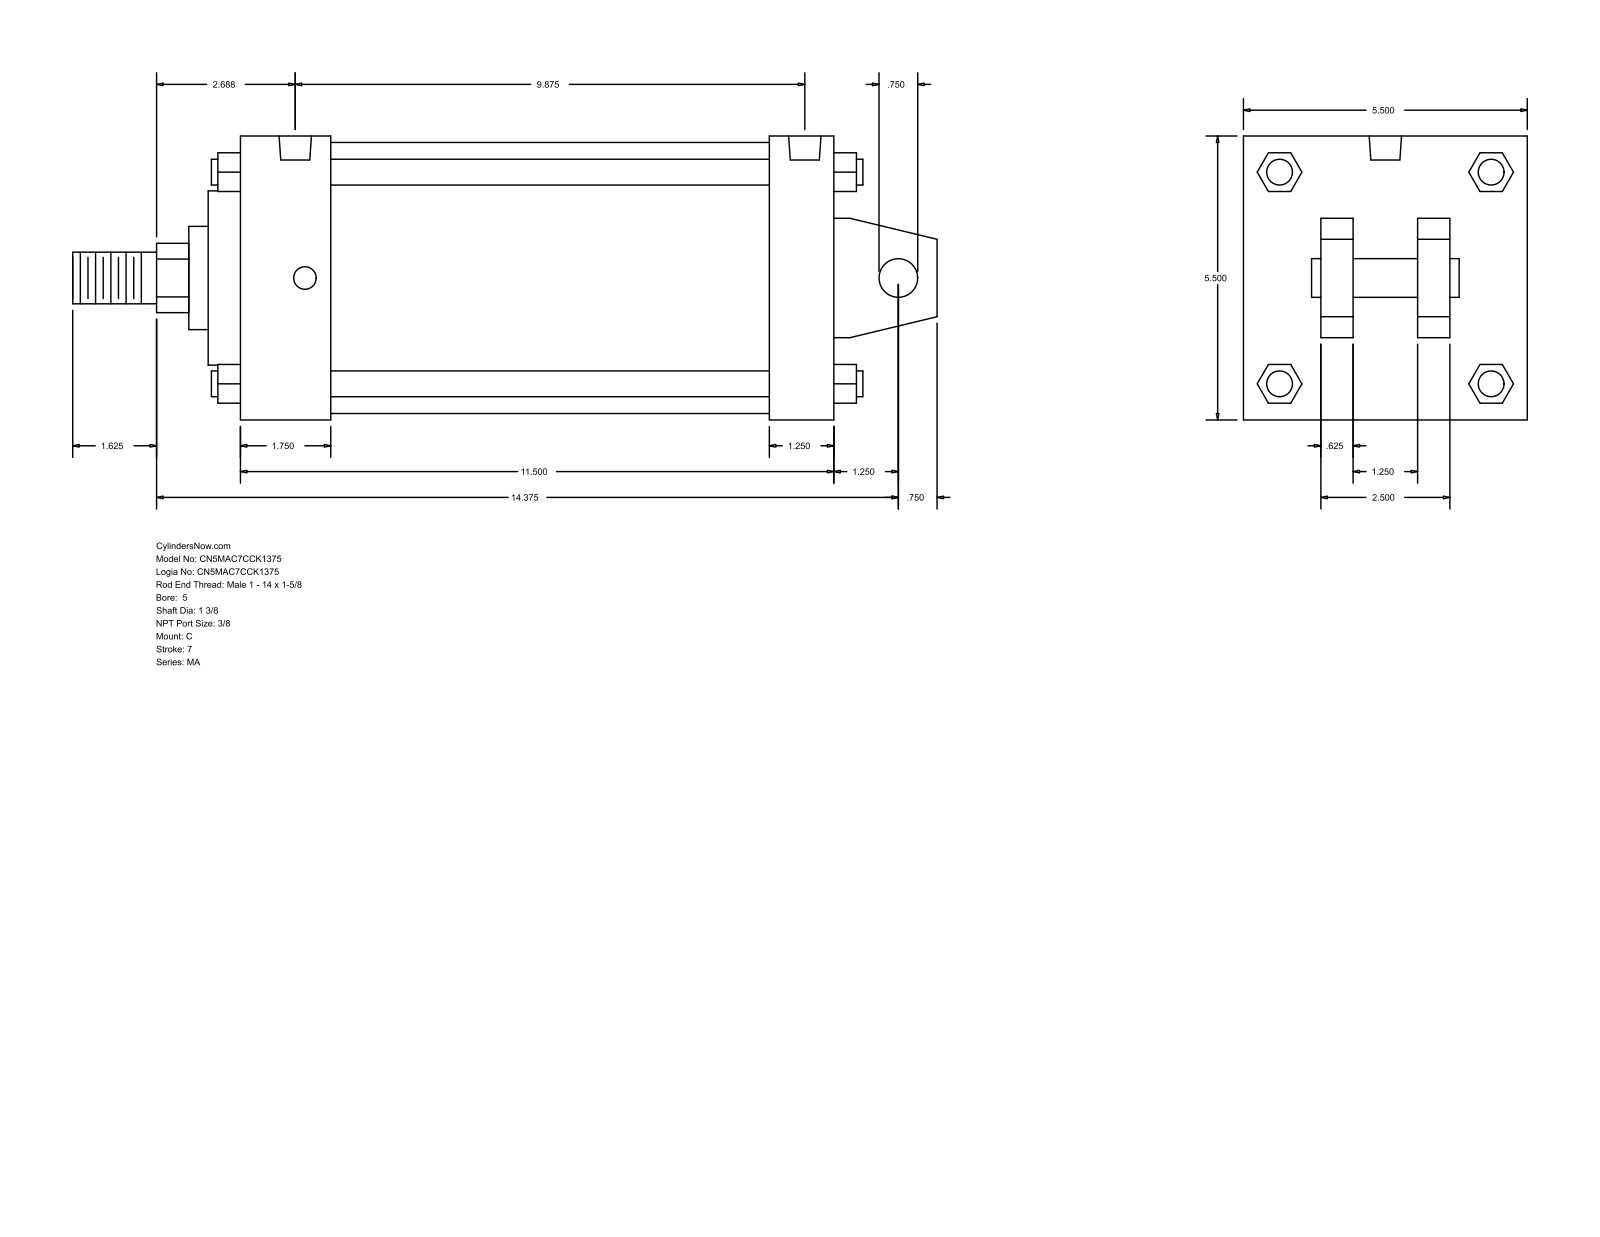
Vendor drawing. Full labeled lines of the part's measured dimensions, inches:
Part name (STEP PRODUCT): MA_C__0500_1.375
STEP written by: GSSL Pune (CONFIG_CONTROL_DESIGN)
Units: inches
Bodies: 0 solids, 141 faces (109 planar, 32 cylindrical, 0 other)
Overall size (bounding box): 16.75 × 5.5 × 5.5
Round holes (diameter × count): ⌀0.437 ×4, ⌀0.627 ×2
Round bosses / shafts (diameter × count): ⌀0.5 ×4, ⌀5.25 ×1, ⌀3.375 ×1, ⌀2 ×1, ⌀1.375 ×1, ⌀1 ×1, ⌀0.75 ×1
Partial cylindrical surfaces — rounded edges, fillets, slot ends (radius × count): R0.672 ×1
Main face-to-face distances: 5.5, 11.5, 0.625, 1.25, 10.25, 1.75, 8.5, 9.75, 2.125, 1.5
Hole centre spacings: 0.188, 9.5, 9.687, 9.875
